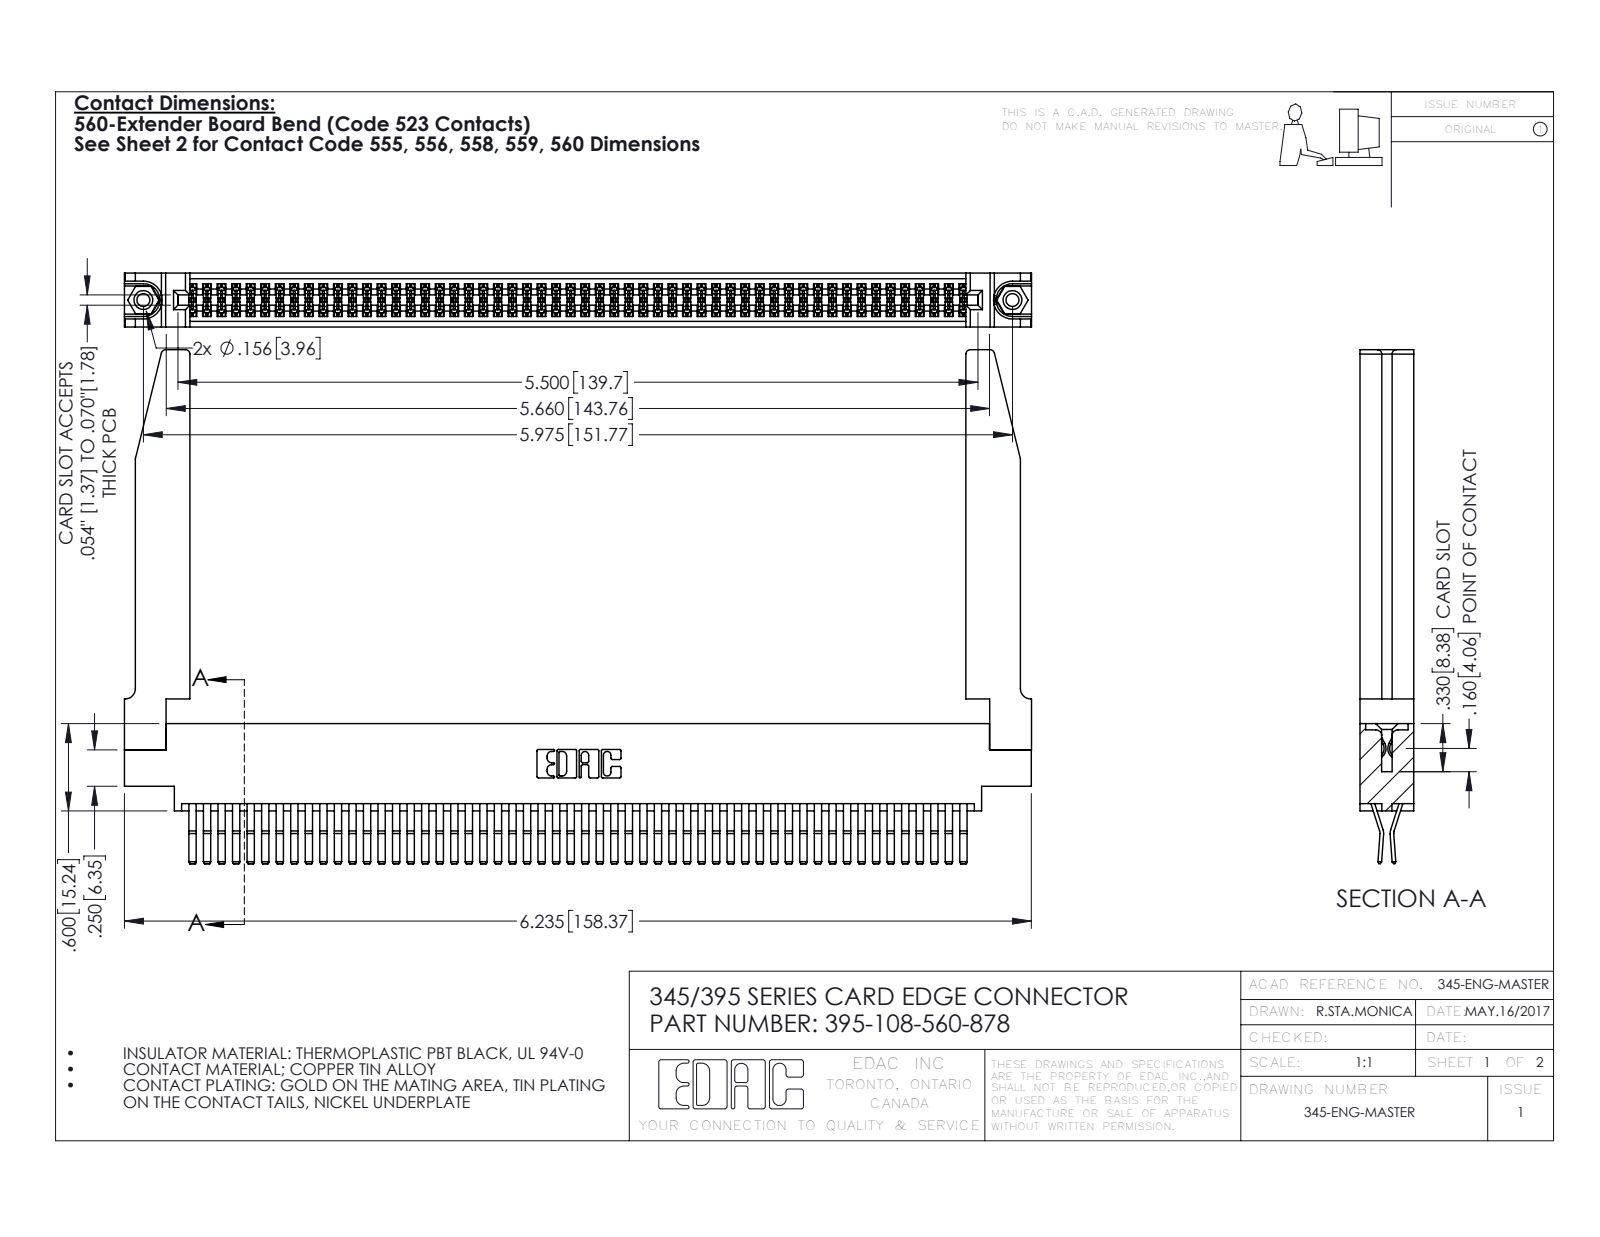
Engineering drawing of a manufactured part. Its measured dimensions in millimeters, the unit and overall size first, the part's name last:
Units: millimetres
Overall size (bounding box): 158.4 × 89.7 × 9.4
Round holes (diameter × count): ⌀2.3 ×2, ⌀3.2 ×2, ⌀4 ×2, ⌀1.6 ×1
Round bosses / shafts (diameter × count): ⌀3.9 ×2
Partial cylindrical surfaces — rounded edges, fillets, slot ends (radius × count): R0.2 ×162, R0.3 ×22, R0.8 ×8, R0.2 ×6, R0.8 ×6, R0.7 ×3, R0.3 ×2, R0.4 ×2
Main face-to-face distances: 9.4, 1.8, 7.6, 0.6, 2.5, 6.9, 5.1, 5.7, 4.4, 3.8
Hole centre spacings: 6.9, 145.8, 151.8
Volume: 23 860 mm³ · Surface area: 32 820 mm²
Bodies: 113 solids, 5980 faces (3790 planar, 2138 cylindrical, 52 other)
Part name (STEP PRODUCT): 345-250-001_345-250-001-102; 395-108-560-878; 345-220-078_345-220-078; 345-292-001_560 Tail (+1 more)
STEP written by: SolidWorks 2016 (CONFIG_CONTROL_DESIGN)
